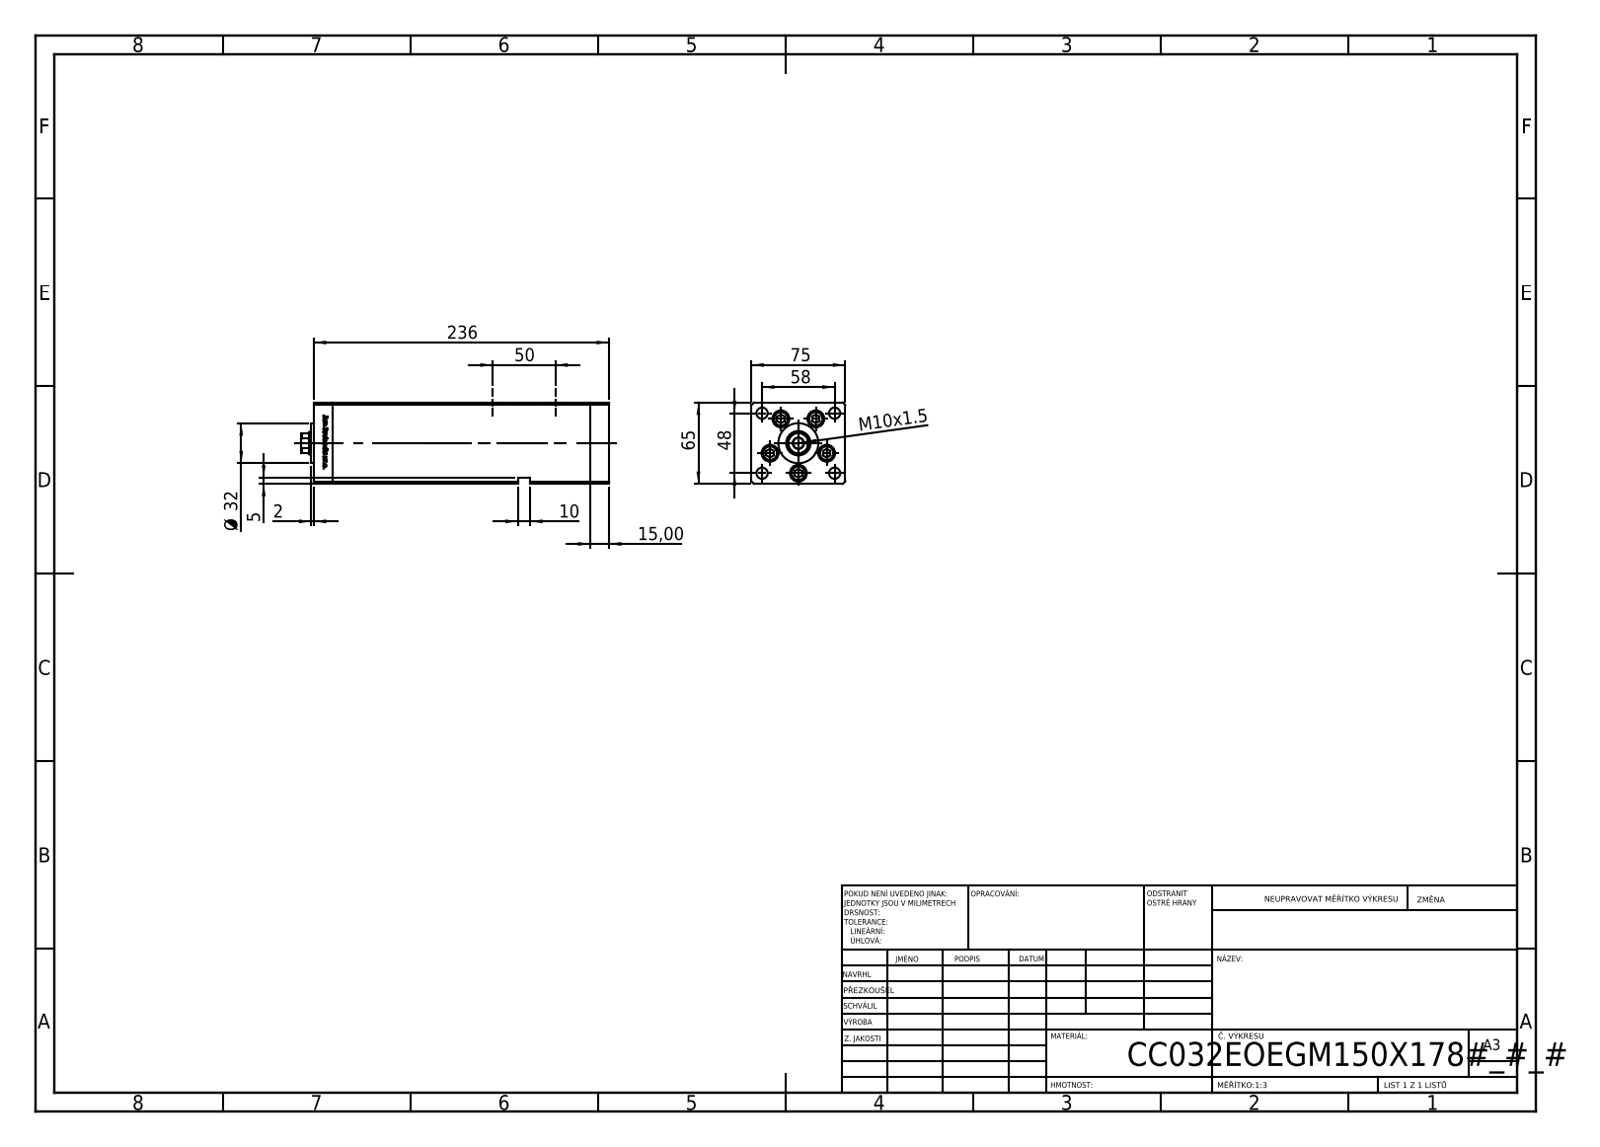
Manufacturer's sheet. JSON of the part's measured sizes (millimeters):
{"part_name": "V220C_E MIDDLE; ALLEN BOLT; V220C_VC_E; V220C BACK_E (+1 more)", "step_written_by": "SolidWorks 2019 (CONFIG_CONTROL_DESIGN)", "units": "millimeters", "bodies": {"solids": 14, "faces": 1212, "planar": 473, "cylindrical": 165, "other": 574}, "overall_size": [246, 75, 65], "volume_mm3": 975804, "surface_area_mm2": 169473, "round_holes": [[9, 9], [13.5, 5], [10.5, 4], [16.5, 4], [2, 2], [13.16, 2], [8.5, 1], [18, 1], [19.5, 1]], "round_bosses_or_shafts": [[12.5, 5], [8, 5], [32, 1]], "partial_cylinders_radius": [[0.93, 2], [8.5, 1]], "face_to_face_distances": [75, 65, 15, 206, 221, 236, 54.5, 10.5, 26.25, 48.75], "hole_center_spacings": [24, 37.64, 58, 15.67, 17.22, 27.71, 28.83, 29]}
